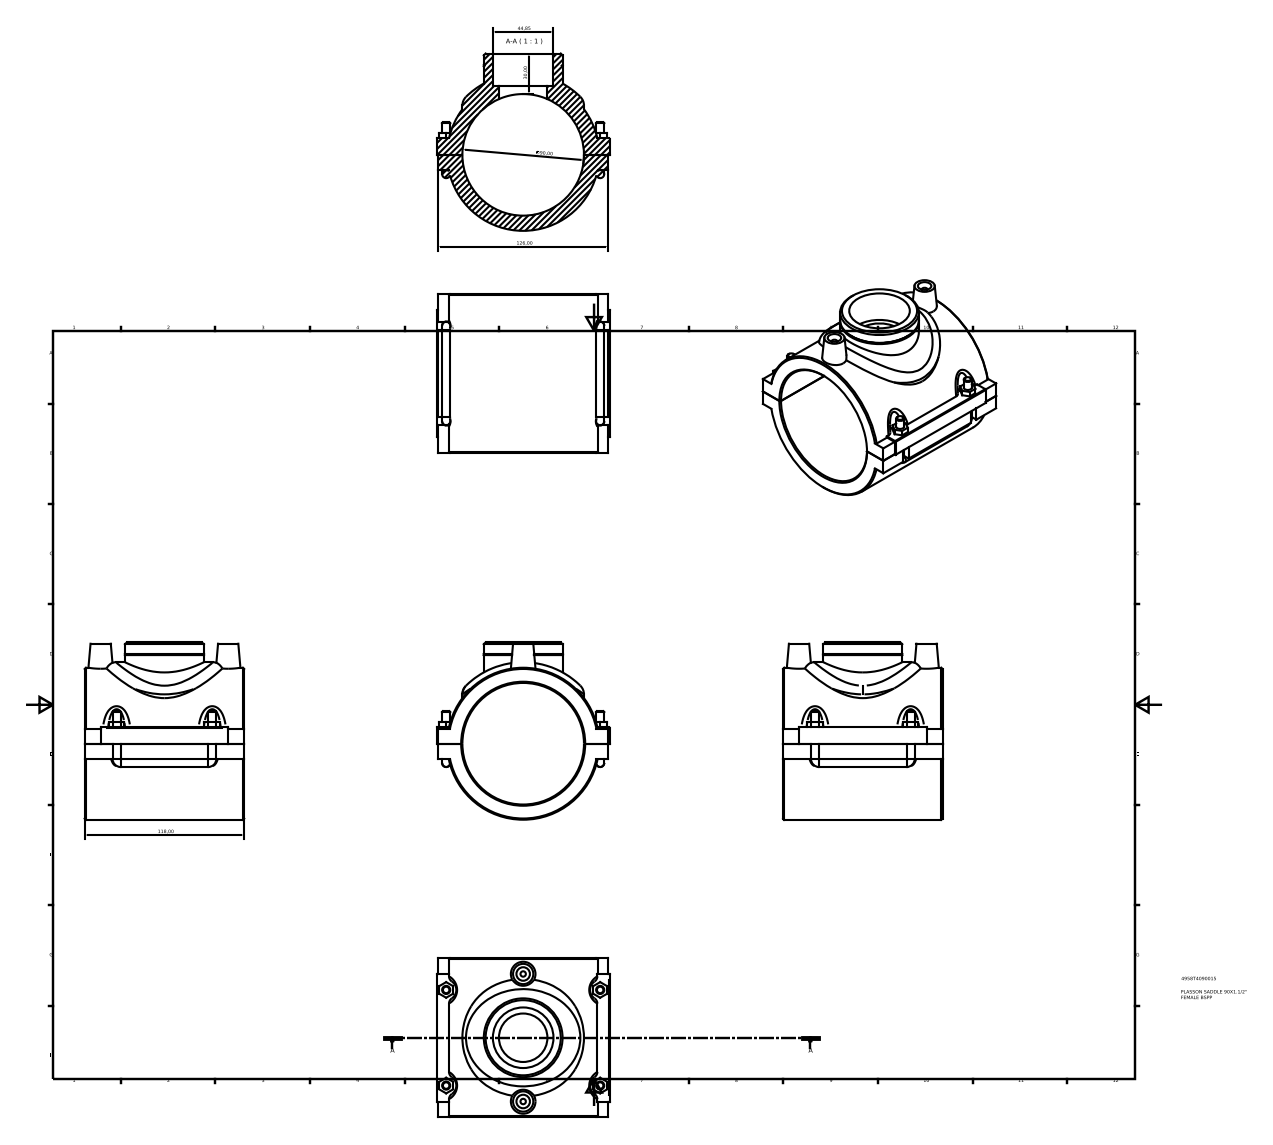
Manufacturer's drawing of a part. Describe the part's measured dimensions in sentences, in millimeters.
The part is named "4958T4090015". Its 3-D file was written by "Autodesk Inventor 2015 (AUTOMOTIVE_DESIGN)". It is 1 solid with 159 faces: 86 planar, 39 cylindrical and 34 other. Overall it measures 131.25 by 128 by 118 millimeters. Its volume is 497 302 cubic millimeters and its surface area 107 318 square millimeters. Round holes: 2 of diameter 10, 1 of diameter 35.88, 1 of diameter 44.84, 1 of diameter 90. Round bosses or shafts: 6 of diameter 6, 2 of diameter 4, 1 of diameter 112.5, 1 of diameter 58.3, 1 of diameter 57.3. Partial cylindrical surfaces (rounded edges, fillets, slot ends): 4 of radius 7.5, 1 of radius 0.5, 1 of radius 45, 1 of radius 60.3. The main face-to-face distances are 118, 1, 127, 11.2, 11.3, 23.5, 12.3, 12.2, 126, 128. The hole center spacings are 47.2, 94.4.
